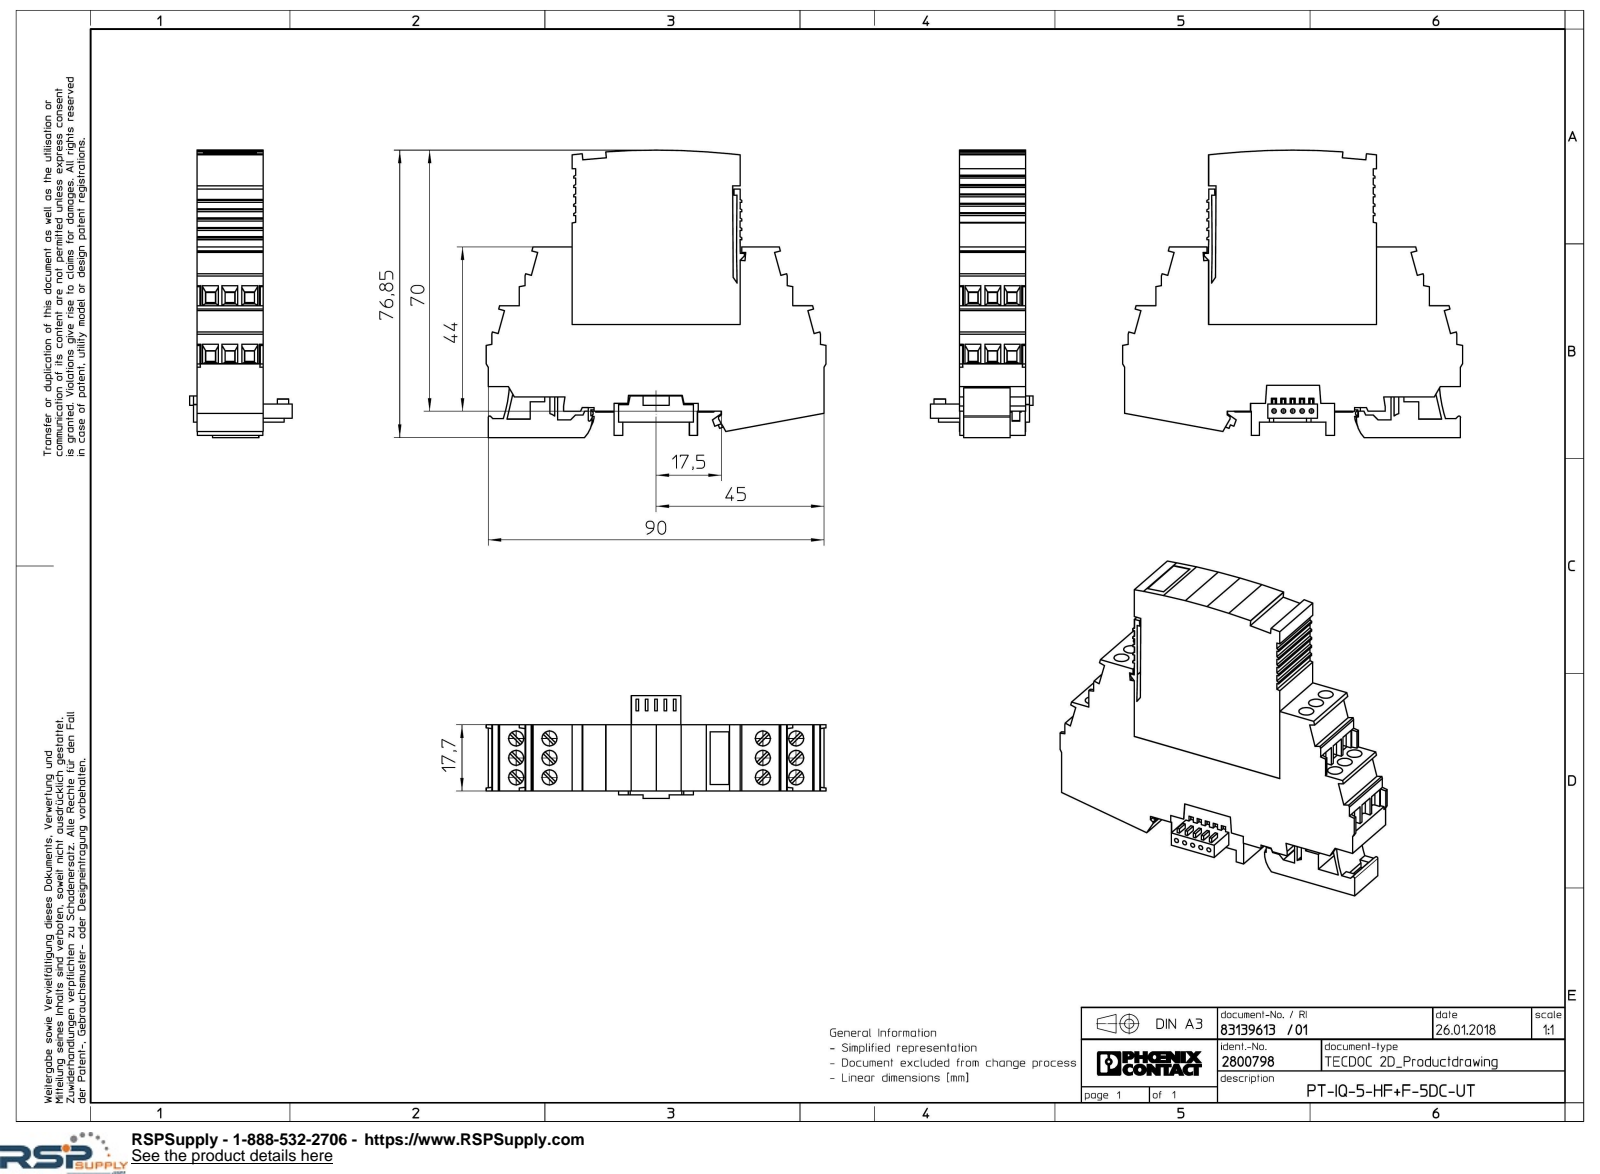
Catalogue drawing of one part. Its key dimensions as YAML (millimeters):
part_name: "PT_IQ_5_HF_F..._UT-select"
step_written_by: "Creo Elements/Direct Modeling 20.1A 29-Sep-2018 (C) Parametric Technology GmbH (AUTOMOTIVE_DESIGN)"
units: millimeters
bodies: {solids: 1, faces: 719, planar: 676, cylindrical: 41, other: 2}
overall_size: [91.05, 76.86, 27.48]
volume: 84136
surface_area: 21405
round_holes:
  - {diameter: 4, count: 12}
  - {diameter: 1.2, count: 5}
partial_cylinders:
  - {radius: 0.3, count: 1}
  - {radius: 0.4, count: 1}
  - {radius: 4, count: 1}
  - {radius: 9.5, count: 1}
  - {radius: 36.42, count: 1}
face_to_face_distances: [17.7, 17.69, 4.15, 15.7, 3.8, 67.5, 22.5, 10.85, 50.98, 46.83]
hole_center_spacings: [5.2, 8.9, 66.1, 66.3, 2.5, 10.3, 10.31, 66.91]
